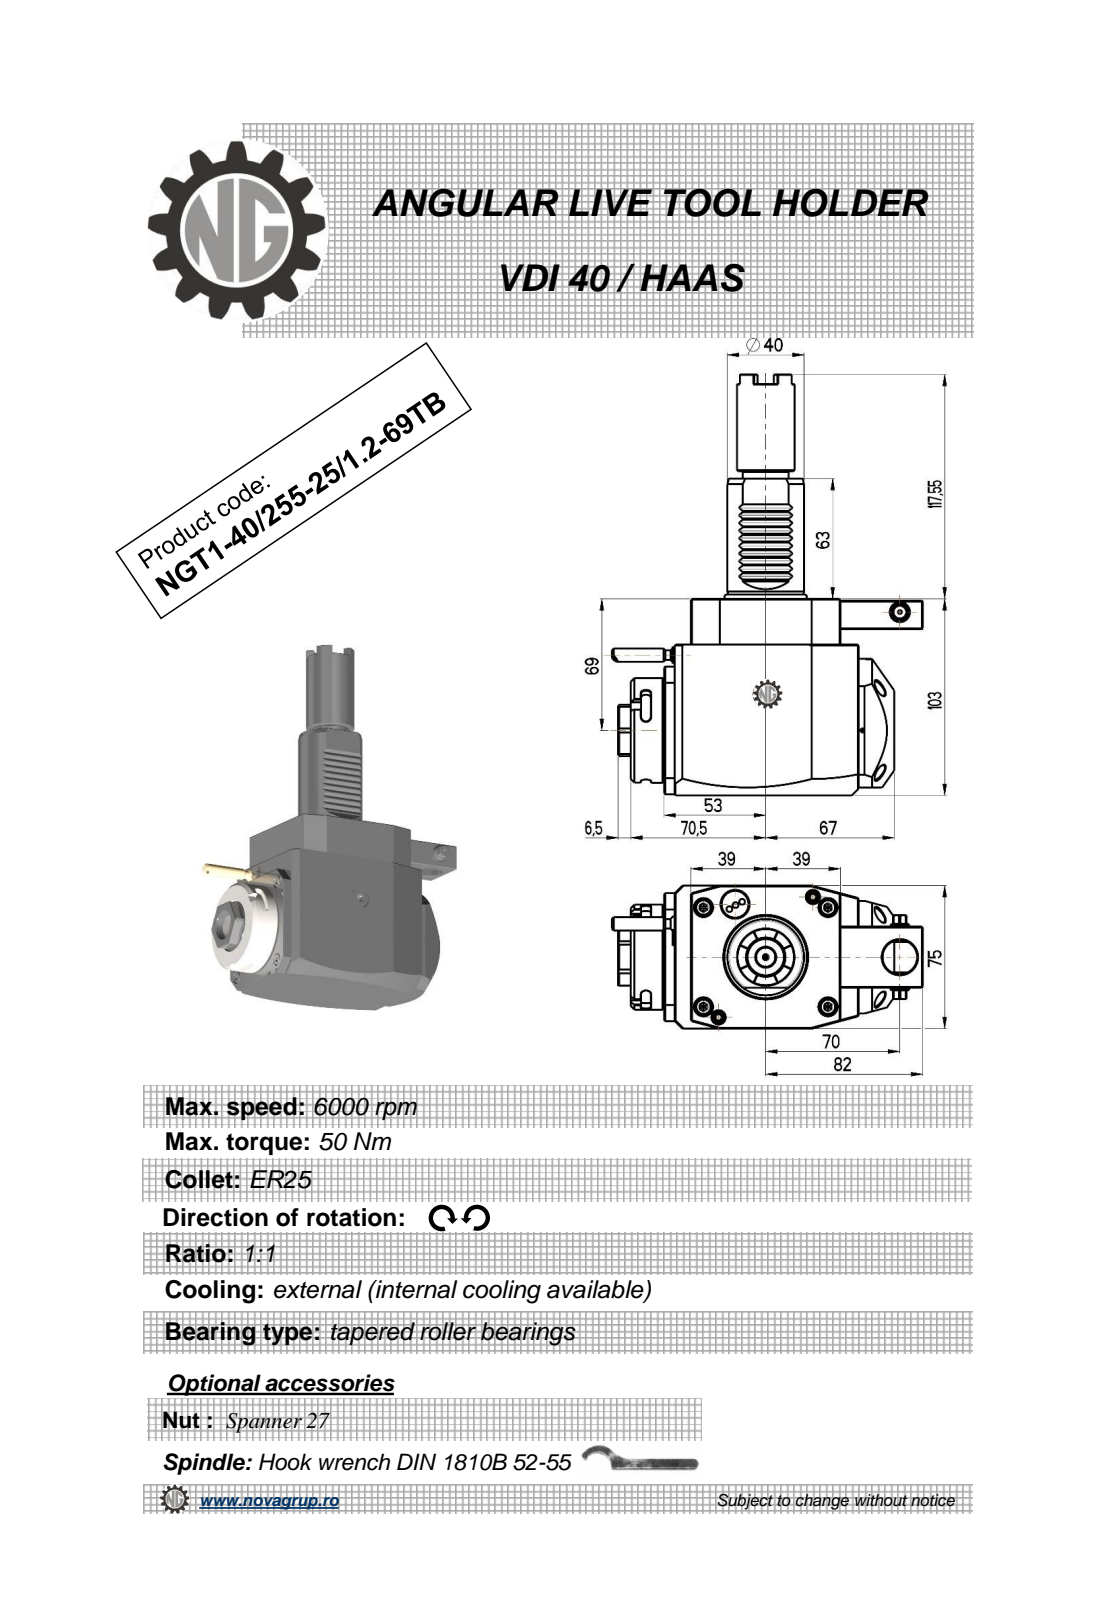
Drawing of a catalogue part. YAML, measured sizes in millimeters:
part_name: "NGT1_40_255_25_1_2_69TB"
step_written_by: "PRO/ENGINEER BY PARAMETRIC TECHNOLOGY CORPORATION, 2010280 (CONFIG_CONTROL_DESIGN)"
units: millimeters
bodies: {solids: 1, faces: 393, planar: 213, cylindrical: 92, other: 88}
overall_size: [220.55, 162.33, 75]
volume: 935476
surface_area: 74644
round_holes:
  - {diameter: 18, count: 2}
  - {diameter: 2, count: 1}
  - {diameter: 2.5, count: 1}
  - {diameter: 3, count: 1}
  - {diameter: 9.5, count: 1}
  - {diameter: 20, count: 1}
round_bosses_or_shafts:
  - {diameter: 8.96, count: 2}
  - {diameter: 55, count: 1}
  - {diameter: 48, count: 1}
  - {diameter: 40, count: 1}
  - {diameter: 30, count: 1}
  - {diameter: 24, count: 1}
  - {diameter: 10, count: 1}
  - {diameter: 7, count: 1}
partial_cylinders:
  - {radius: 0.3, count: 10}
  - {radius: 2.5, count: 6}
  - {radius: 180, count: 2}
  - {radius: 0.5, count: 1}
  - {radius: 3.85, count: 1}
  - {radius: 4.25, count: 1}
  - {radius: 15, count: 1}
  - {radius: 24.5, count: 1}
face_to_face_distances: [75, 103, 17.5, 23, 79, 102, 24, 31.5, 14, 87]
hole_center_spacings: [28.11, 43.2, 61.5, 70]
